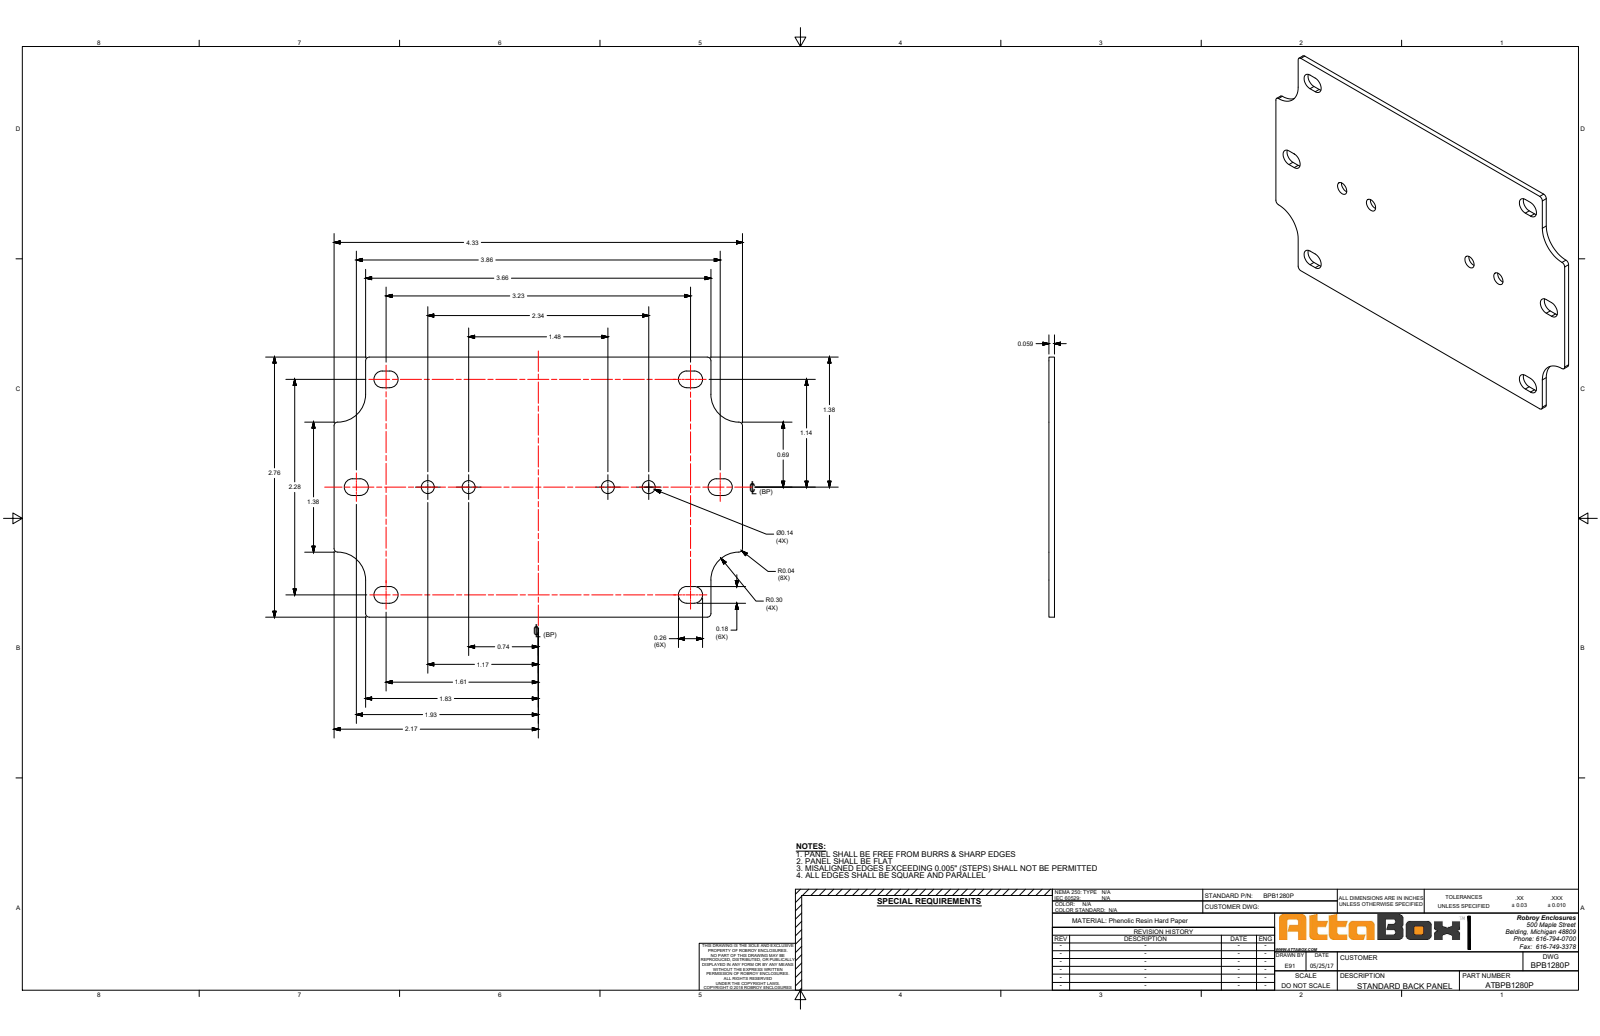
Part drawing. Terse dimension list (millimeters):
name: BPB1280P
written by: SolidWorks 2018 (AUTOMOTIVE_DESIGN)
unit: mm
bodies: 1 solid, 50 faces (22 planar, 28 cylindrical, 0 other)
size: 110 × 70 × 1.5
volume: 10 400 mm³; area: 14 670 mm²
holes: 4× ⌀3.5
rounds: 12× R2.3, 8× R1, 4× R7.5
face distances: 1.5, 70, 8.5, 101.5, 110, 93, 29, 4.5, 3.8, 8.3
hole spacings: 11, 48.5, 37.5, 59.5
